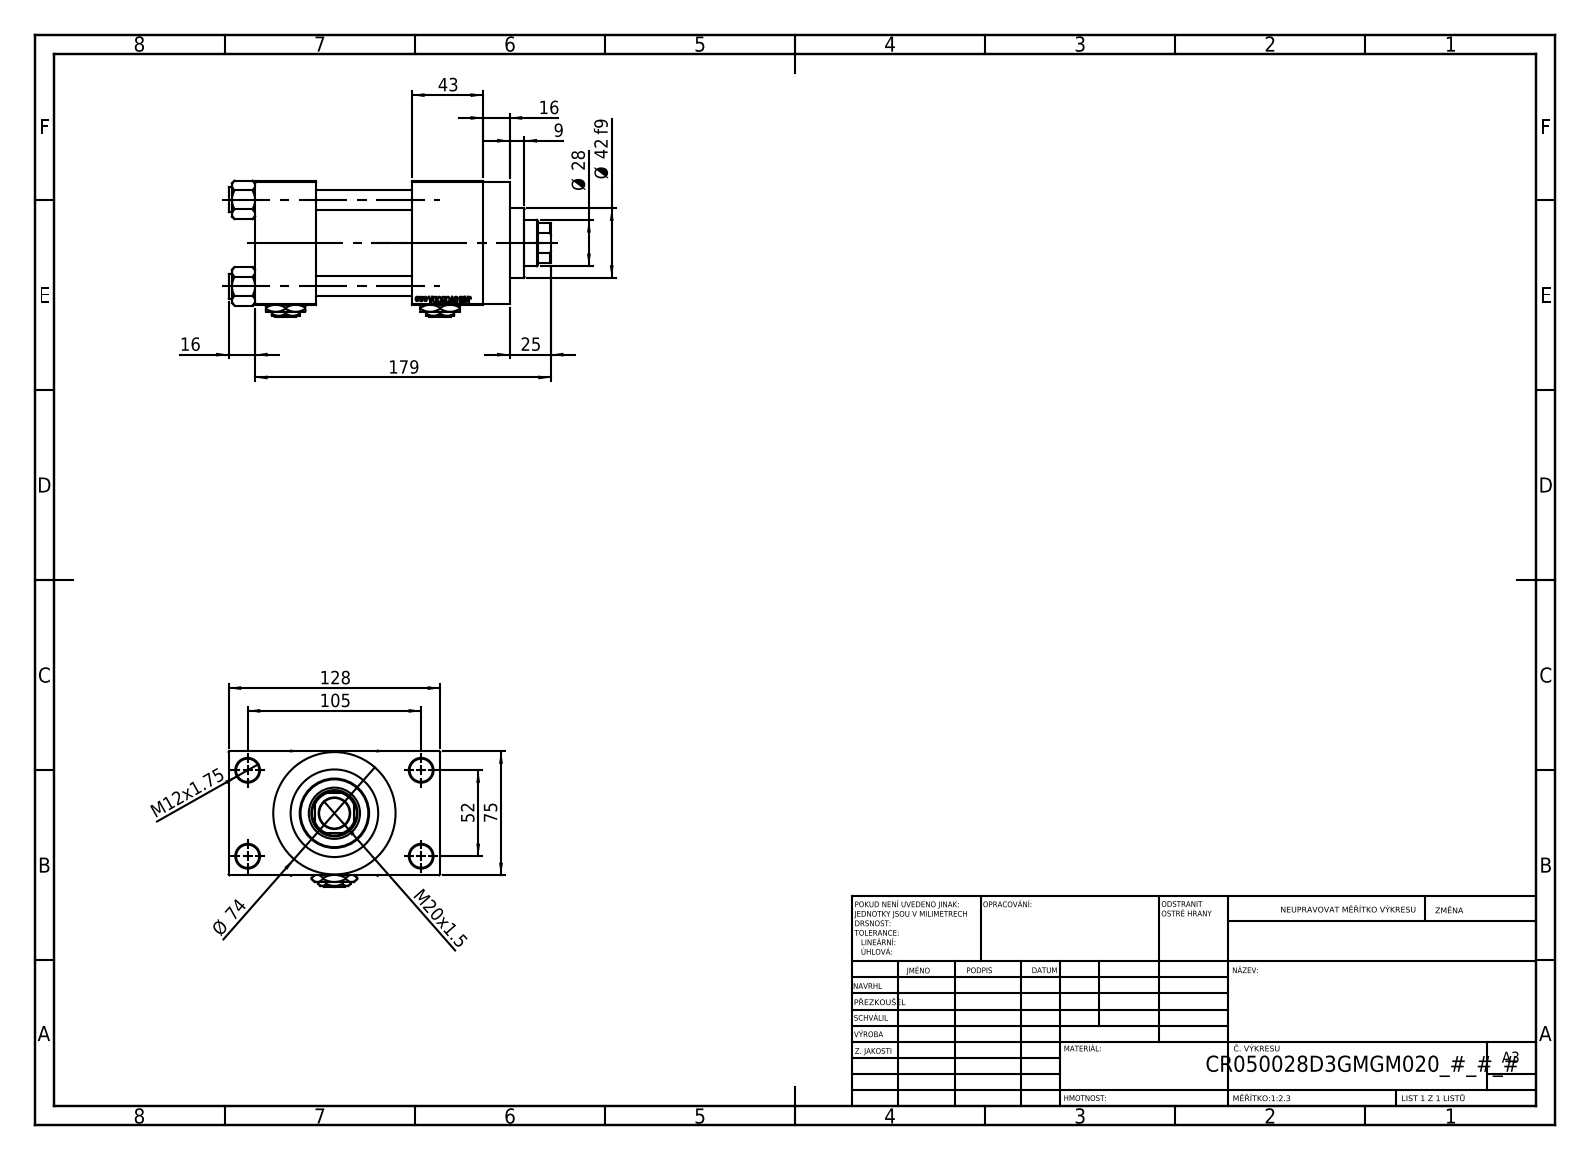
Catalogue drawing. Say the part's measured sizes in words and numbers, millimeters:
The part is named "Zatka_pro_OIL_PORT; V215CR_D_Body; V215CR_D_TYCINKA; V215CR_VCP_D (+2 more)". Its 3-D file was written by "SolidWorks 2019 (CONFIG_CONTROL_DESIGN)". It is 13 solids with 1204 faces: 545 planar, 99 cylindrical and 560 other. Overall it measures 195 by 128 by 82.27 millimeters. Its volume is 802 226 cubic millimeters and its surface area 174 728 square millimeters. Round holes: 4 of diameter 12, 4 of diameter 14, 4 of diameter 20.96, 4 of diameter 30, 3 of diameter 7, 1 of diameter 18.5, 1 of diameter 28, 1 of diameter 31, 1 of diameter 41, 1 of diameter 50, 1 of diameter 53. Round bosses or shafts: 4 of diameter 15, 1 of diameter 74, 1 of diameter 56, 1 of diameter 42. Partial cylindrical surfaces (rounded edges, fillets, slot ends): 1 of radius 13.5. The main face-to-face distances are 75, 58, 37, 95, 26.5, 138, 101, 43, 101.5, 16. The hole center spacings are 26.35, 36.98, 52.3, 58.43, 58.59, 78.65, 94.37, 52.
